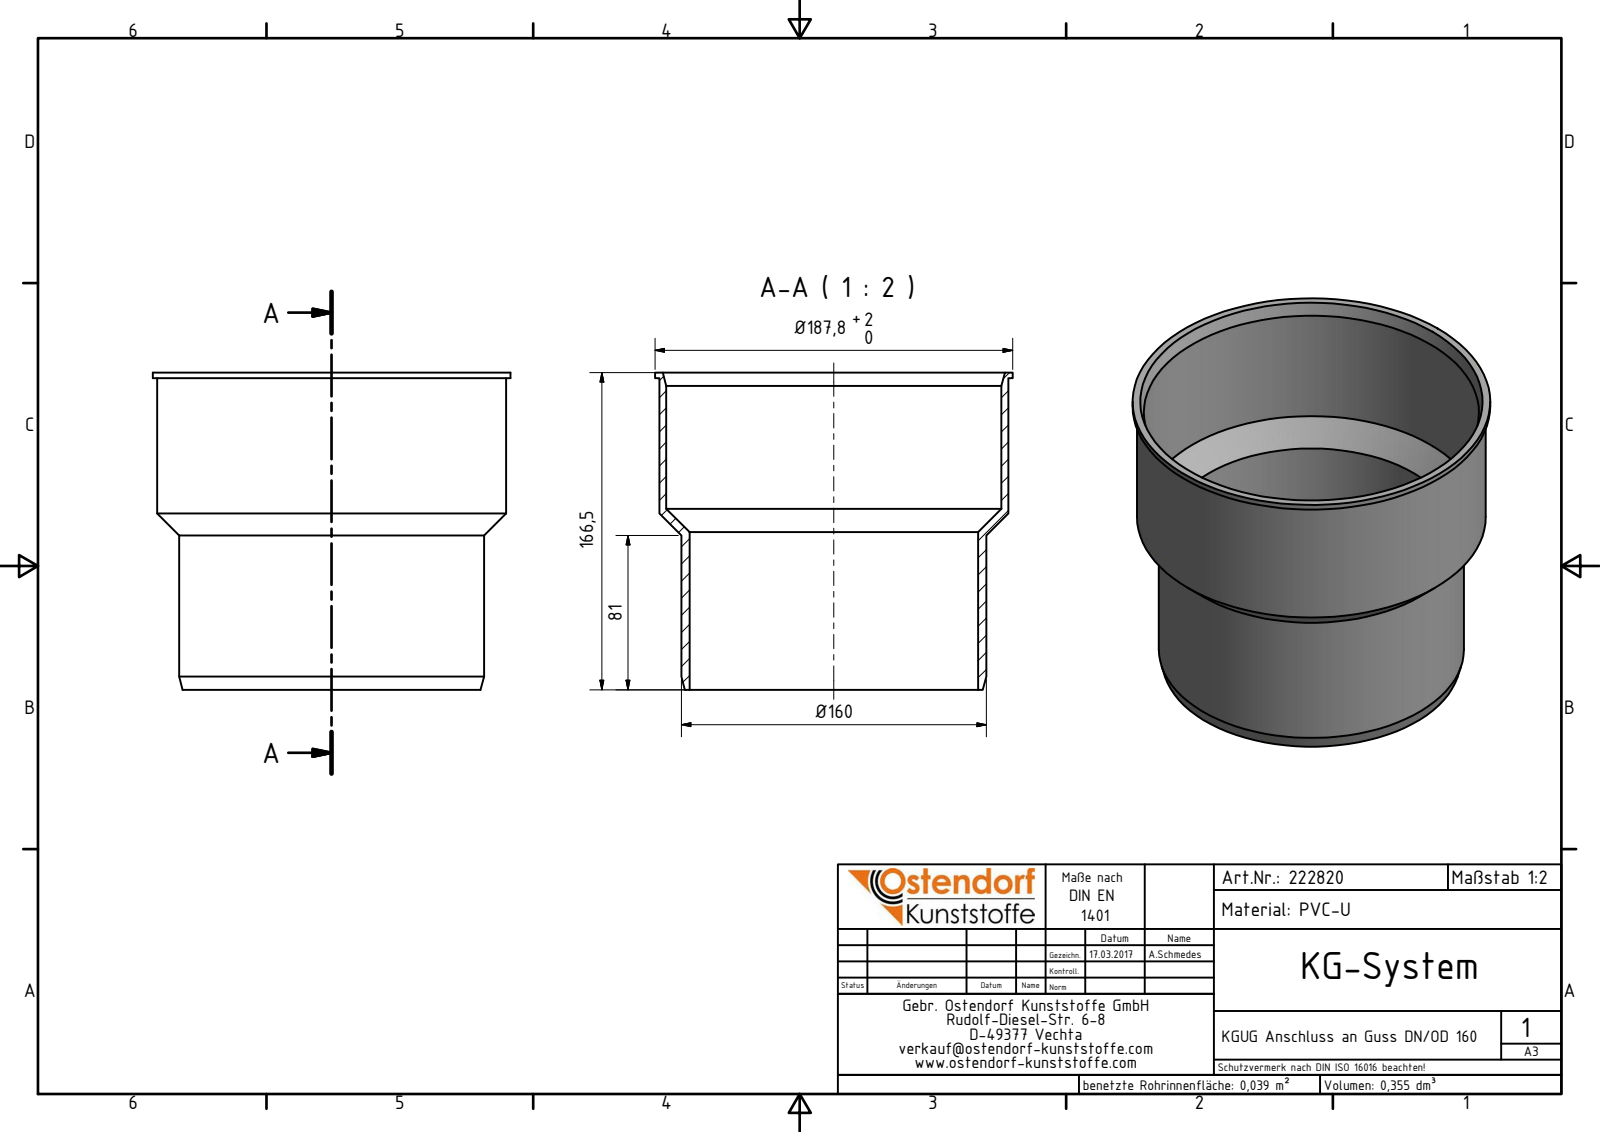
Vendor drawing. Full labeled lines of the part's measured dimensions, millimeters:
Part name (STEP PRODUCT): 222820 KGUG Anschluss an Guss DN_OD 160
STEP written by: Autodesk Inventor 2016 (AUTOMOTIVE_DESIGN)
Units: millimetres
Bodies: 1 solid, 12 faces (3 planar, 5 cylindrical, 4 other)
Overall size (bounding box): 187.8 × 187.8 × 166.5
Volume: 355 310 mm³ · Surface area: 185 118 mm²
Round holes (diameter × count): ⌀151.6 ×1, ⌀176 ×1
Round bosses / shafts (diameter × count): ⌀187.8 ×1, ⌀183.2 ×1, ⌀160.2 ×1
Main face-to-face distances: 3, 163.5, 166.5
